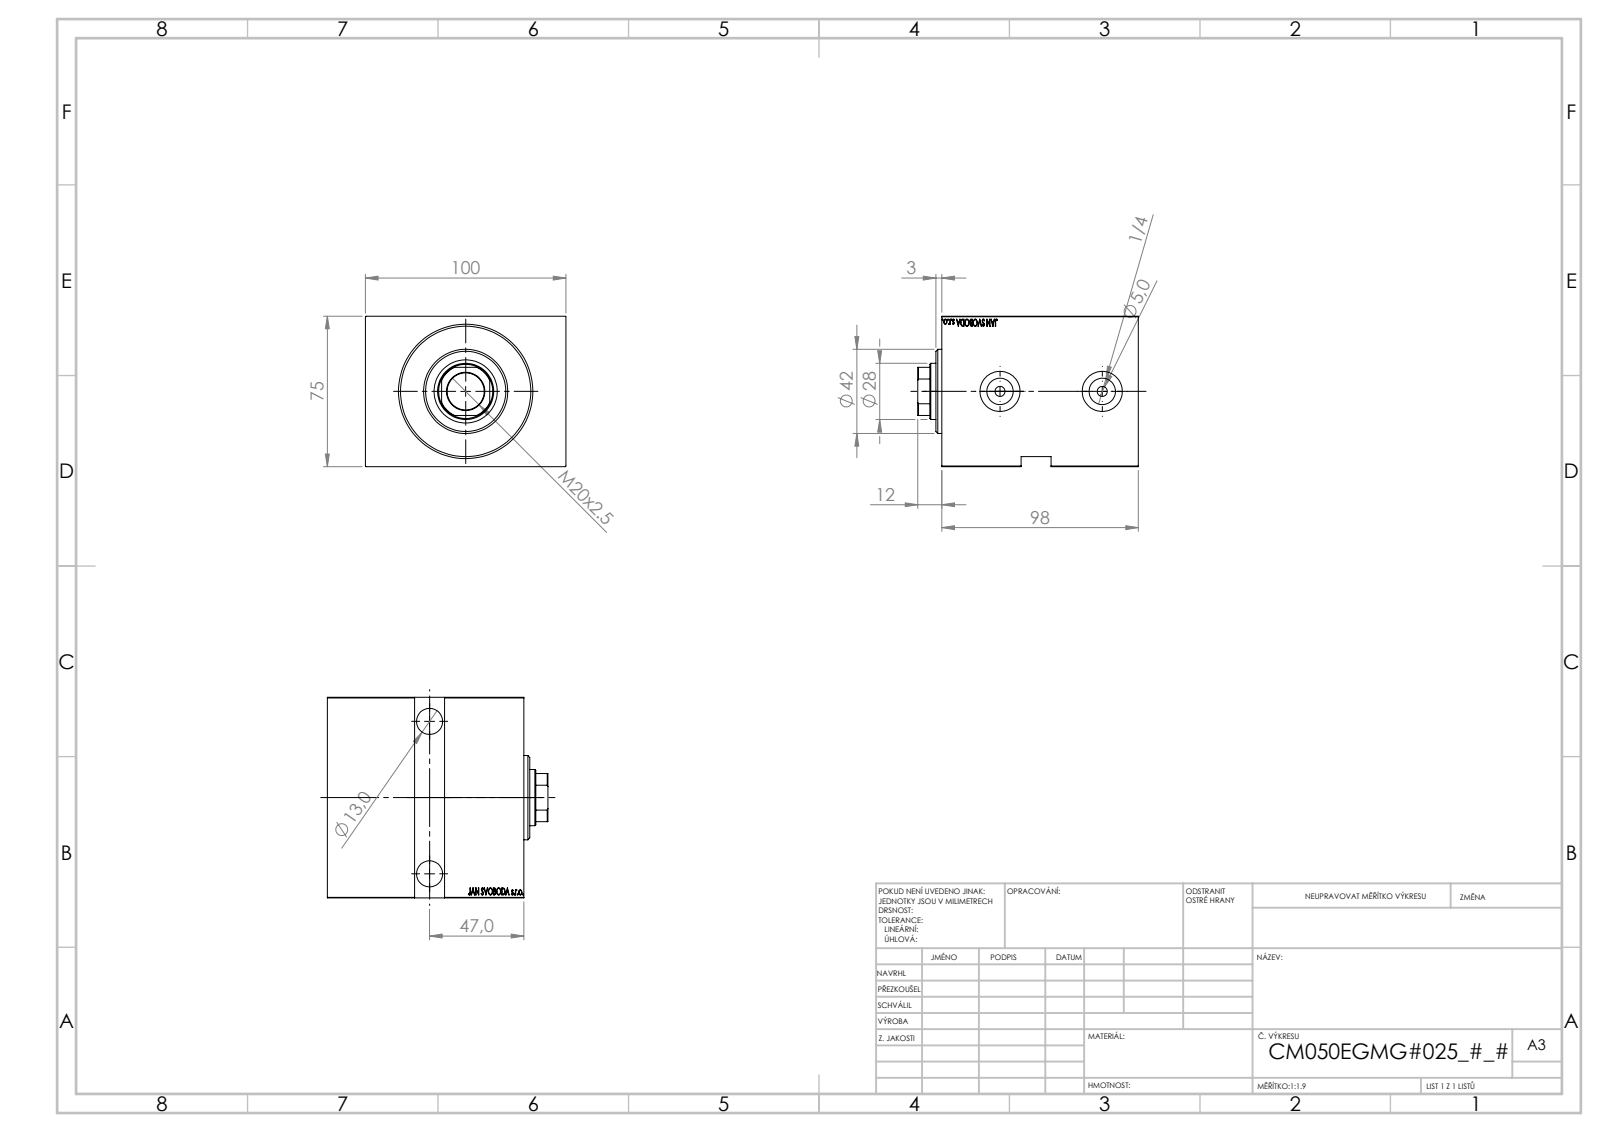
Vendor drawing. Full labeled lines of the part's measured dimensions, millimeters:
Part name (STEP PRODUCT): V450CM_E_VCP; V450CM_VC_B; V450CM_E_Body
STEP written by: SolidWorks 2019 (CONFIG_CONTROL_DESIGN)
Units: millimetres
Bodies: 3 solids, 851 faces (411 planar, 46 cylindrical, 394 other)
Overall size (bounding box): 110 × 100 × 75
Volume: 647 015 mm³ · Surface area: 97 266 mm²
Round holes (diameter × count): ⌀5 ×2, ⌀13 ×2, ⌀13.16 ×2, ⌀19 ×2, ⌀20 ×2, ⌀18.5 ×1, ⌀28 ×1, ⌀31.5 ×1, ⌀50 ×1, ⌀52 ×1, ⌀65 ×1
Round bosses / shafts (diameter × count): ⌀42 ×1
Partial cylindrical surfaces — rounded edges, fillets, slot ends (radius × count): R13.5 ×1
Main face-to-face distances: 75, 100, 98, 14, 84, 5, 93, 79, 81.4, 67.4
Hole centre spacings: 51, 76
